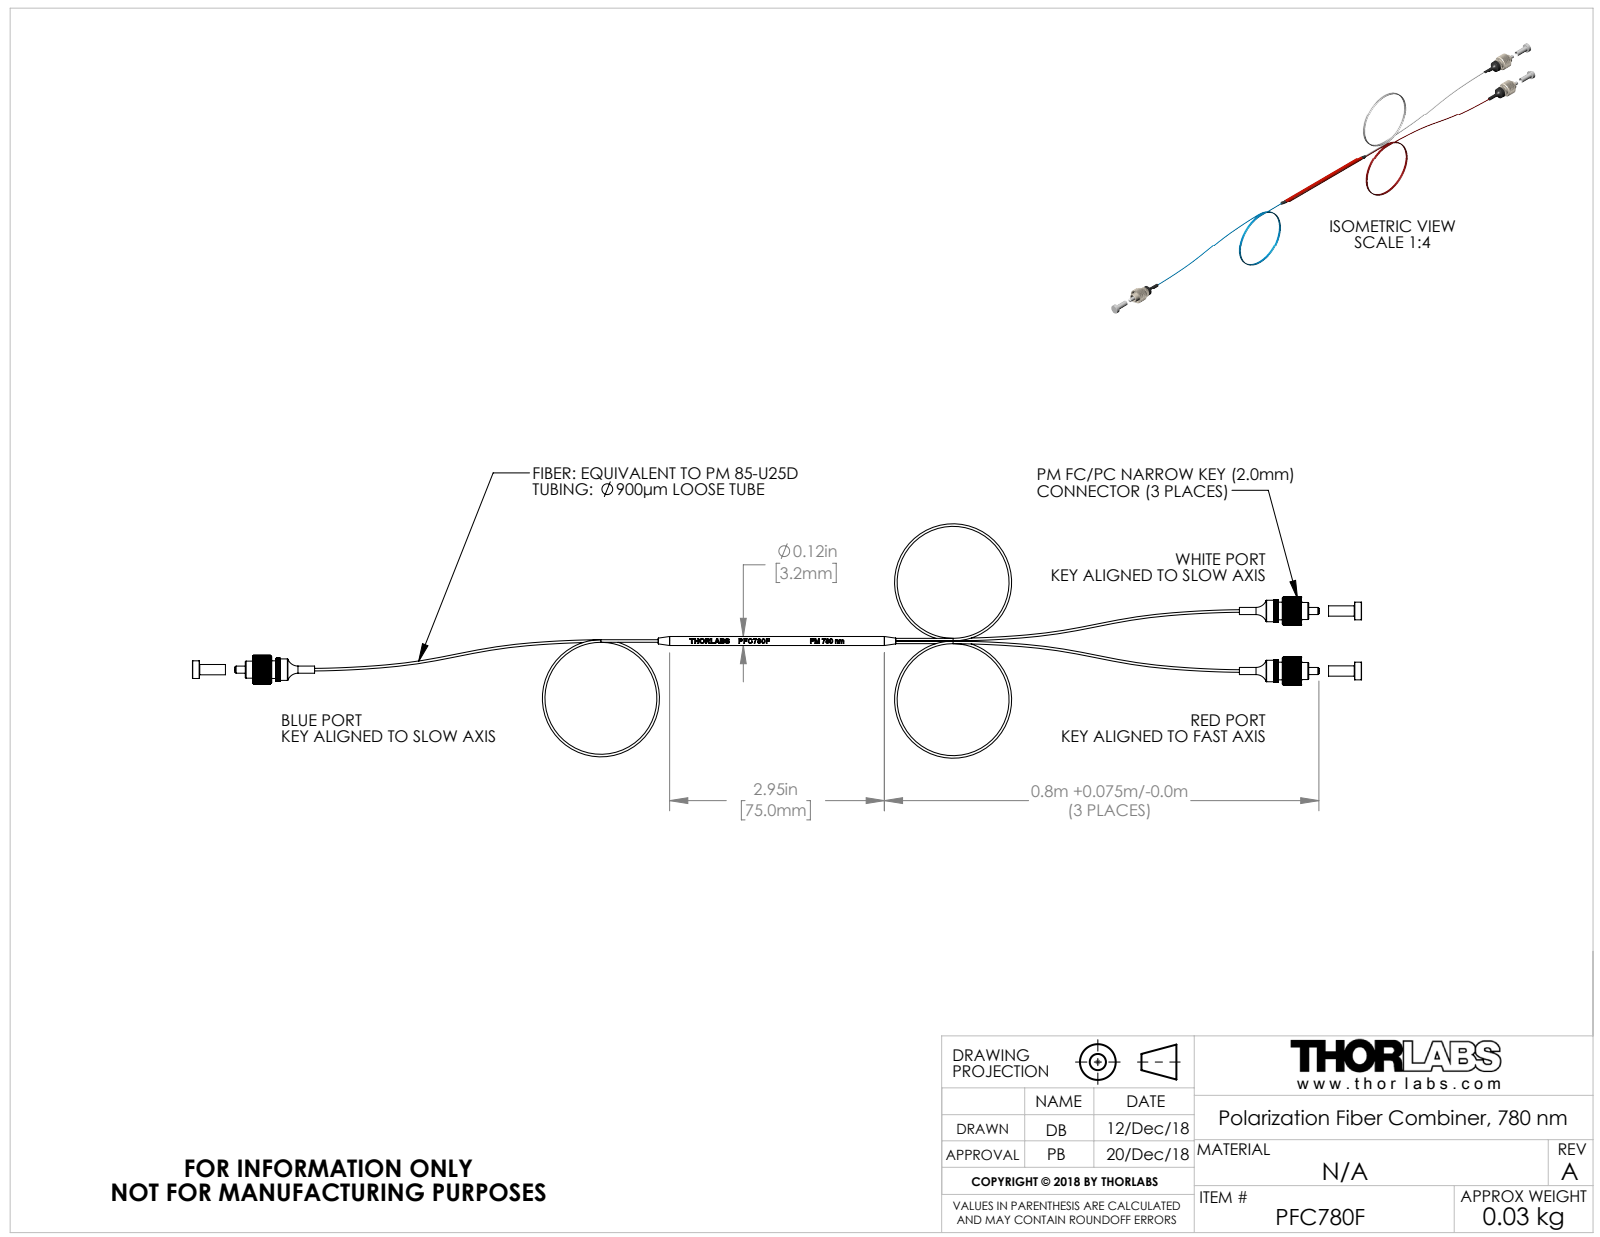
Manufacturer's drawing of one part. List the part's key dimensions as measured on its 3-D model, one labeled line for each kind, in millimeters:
Part name (STEP PRODUCT): DWG1529; DWG1540; DWG1553; DWG1528 (+8 more)
STEP written by: SolidWorks 2018 (CONFIG_CONTROL_DESIGN)
Units: millimetres
Bodies: 32 solids, 2607 faces (1271 planar, 886 cylindrical, 450 other)
Overall size (bounding box): 408.3 × 81.85 × 14.2
Volume: 3 273 mm³ · Surface area: 13 572 mm²
Round holes (diameter × count): ⌀0.5 ×6, ⌀0.9 ×3, ⌀0.95 ×3, ⌀1 ×3, ⌀2.5 ×3, ⌀2.8 ×3, ⌀3.36 ×3, ⌀4.38 ×3, ⌀4.4 ×3, ⌀5.08 ×3, ⌀5.55 ×3, ⌀6.1 ×3
Round bosses / shafts (diameter × count): ⌀7.5 ×3, ⌀7.07 ×3, ⌀6.17 ×3, ⌀6.08 ×3, ⌀5.95 ×3, ⌀5.38 ×3, ⌀4.85 ×3, ⌀3.6 ×3
Partial cylindrical surfaces — rounded edges, fillets, slot ends (radius × count): R0.5 ×6, R0.75 ×3, R1.55 ×3, R2.26 ×3, R3.98 ×3, R5 ×3, R0.45 ×2, R1 ×1
Main face-to-face distances: 6.86, 6.85, 2, 1.43, 4.97, 2.97, 349.97, 1.54, 3.43, 27.68
Hole centre spacings: 10.2, 0.47, 0.48, 0.95, 4.03, 9.74, 10.24, 10.66
